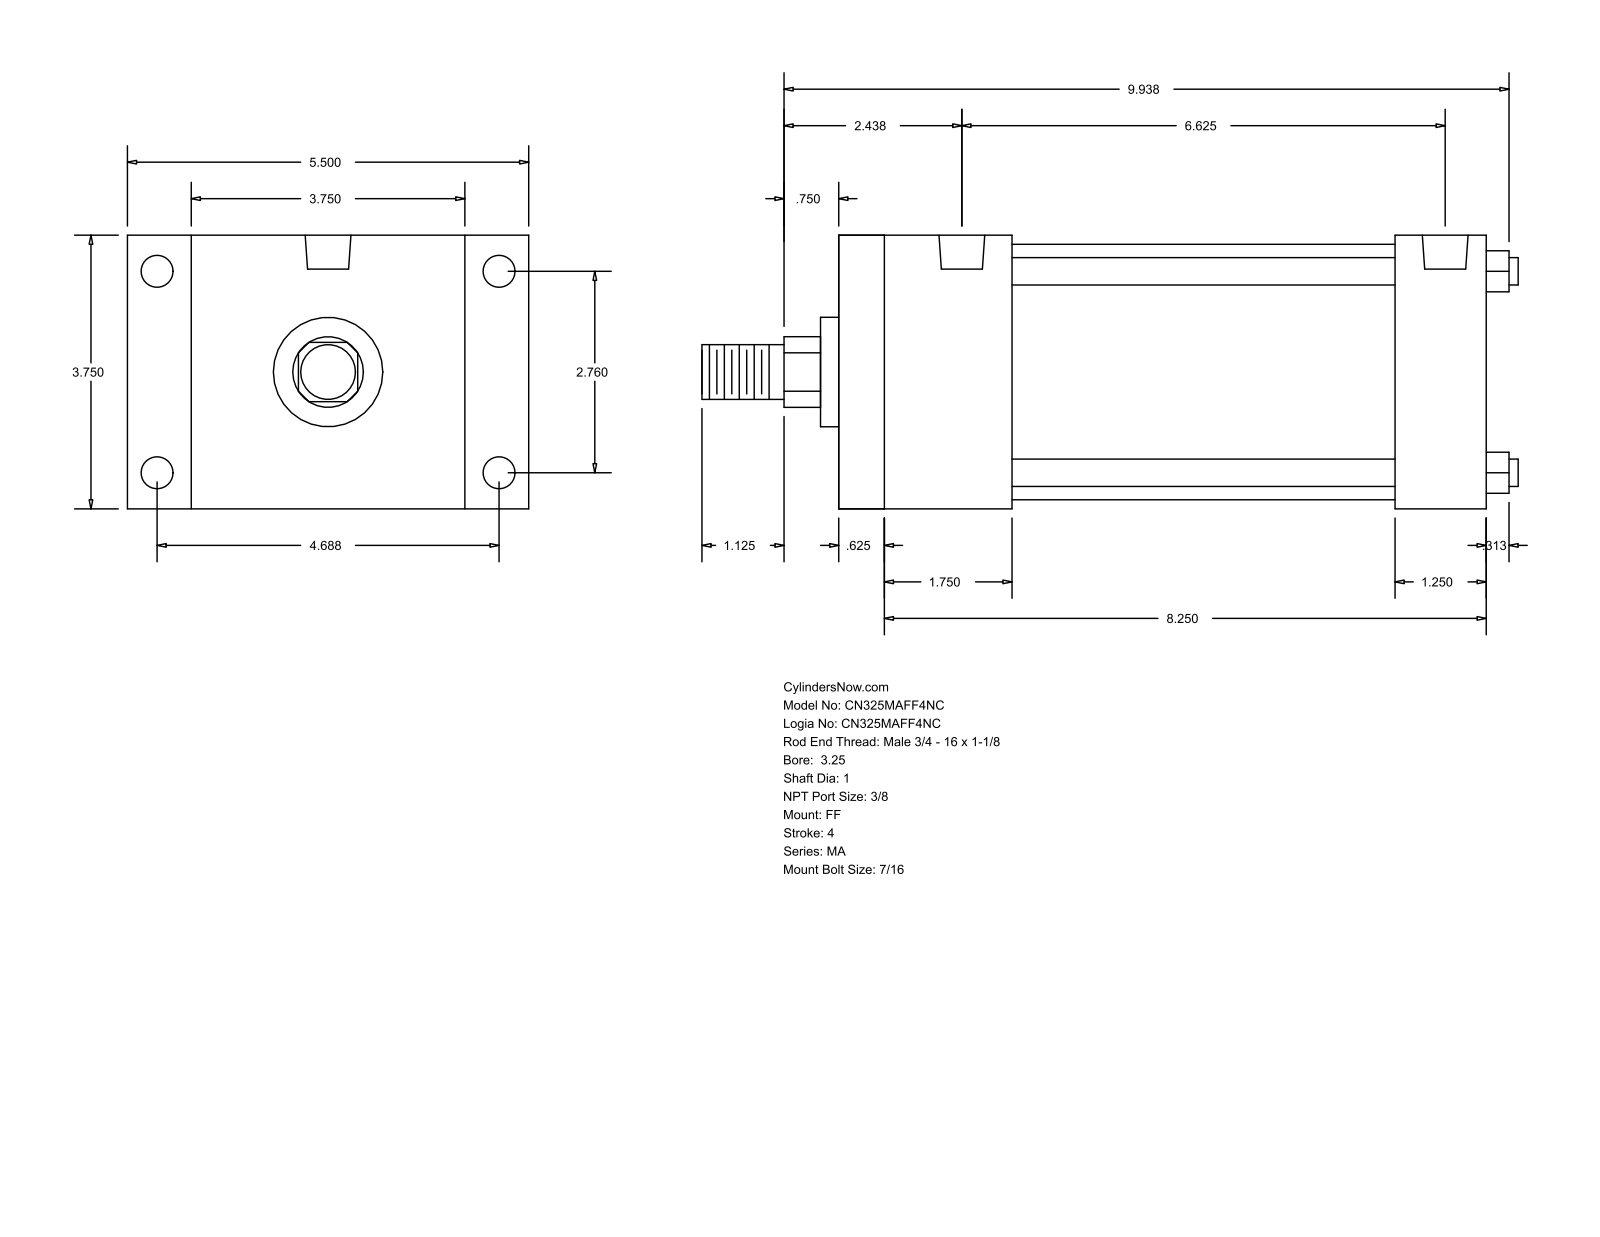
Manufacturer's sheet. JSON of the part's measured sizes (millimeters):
{"part_name": "MA_FF__0325_1", "step_written_by": "GSSL Pune (CONFIG_CONTROL_DESIGN)", "units": "millimeters", "bodies": {"solids": 0, "faces": 92, "planar": 64, "cylindrical": 28, "other": 0}, "overall_size": [284.16, 139.7, 95.25], "round_holes": [[11.11, 8], [15.93, 2]], "round_bosses_or_shafts": [[9.53, 4], [88.9, 1], [38.1, 1], [25.4, 1], [19.05, 1]], "partial_cylinders_radius": [[12.29, 1]], "face_to_face_distances": [95.24, 225.42, 15.87, 209.55, 22.23, 117.47, 60.33, 193.67, 44.46, 177.8], "hole_center_spacings": [4.76, 70.1, 119.06, 138.16, 158.76, 163.52, 168.28]}
